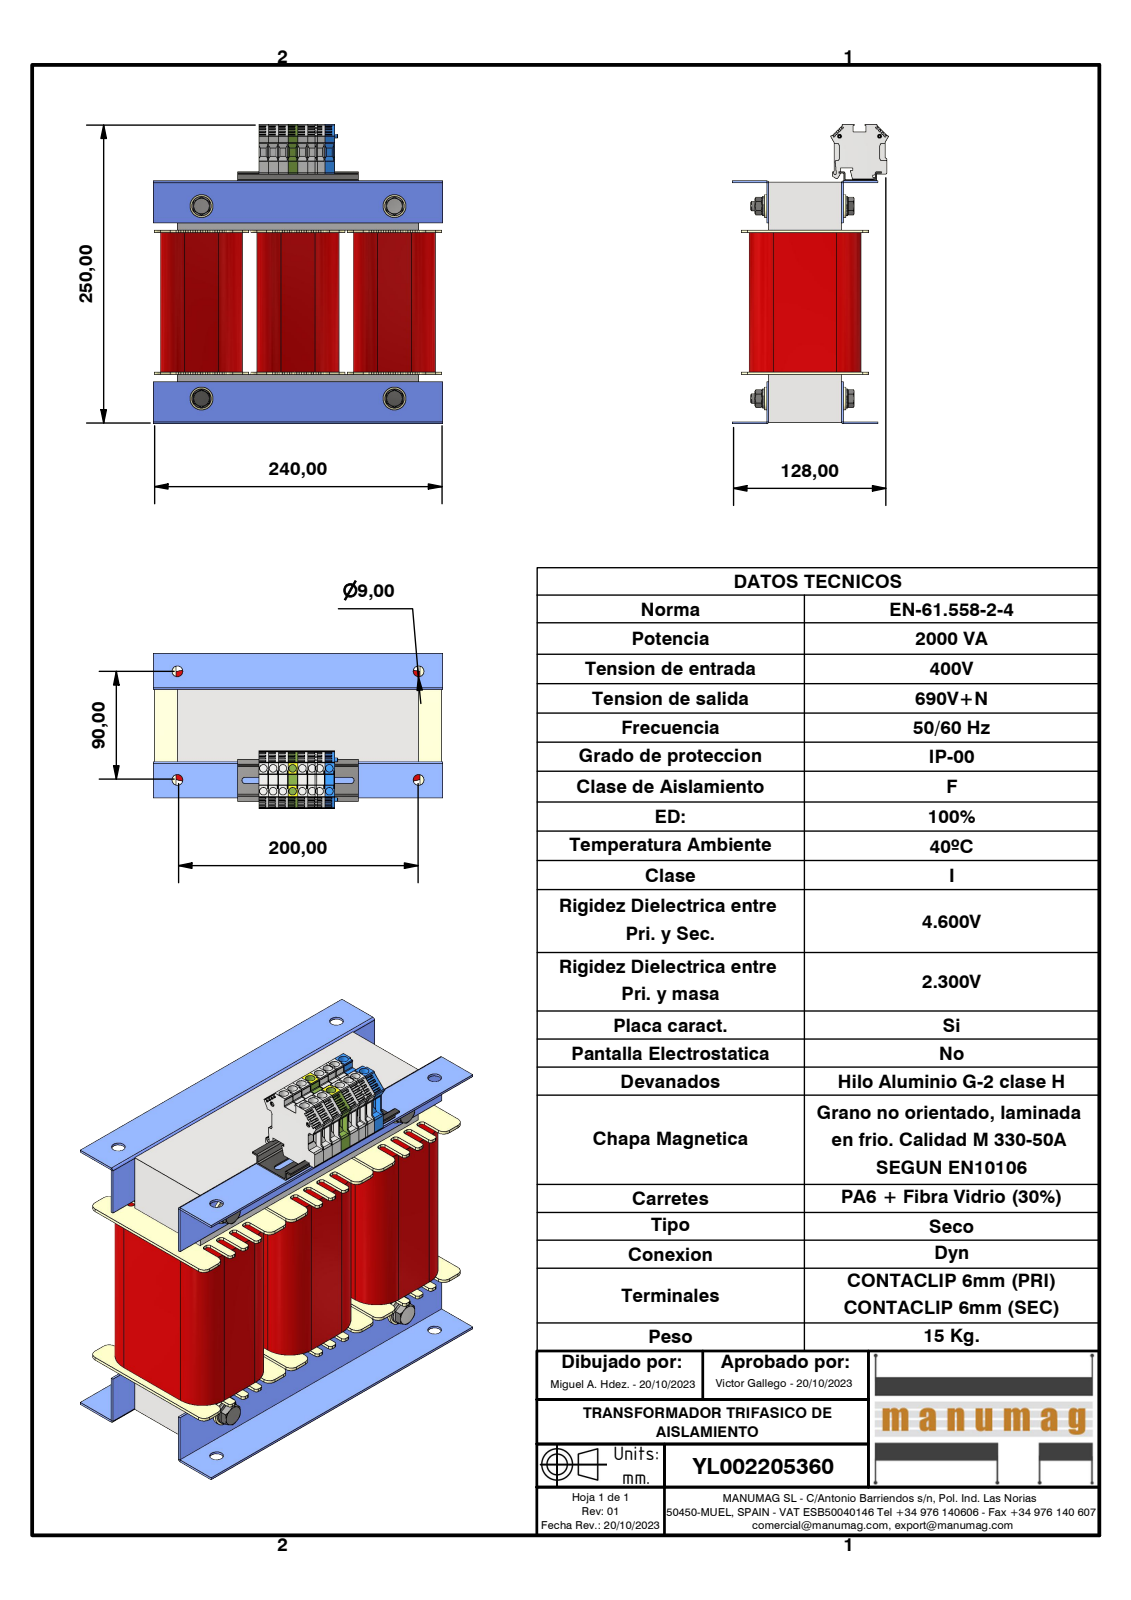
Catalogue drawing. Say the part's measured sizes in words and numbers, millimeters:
The part is named "YL002205360; 3UI120 200 x 200 - 60 (Rc40); UI 120_60; RC40 NT040 (+8 more)". Its 3-D file was written by "Autodesk Inventor 2023 (AUTOMOTIVE_DESIGN)". It is 41 solids with 2898 faces: 2018 planar, 712 cylindrical and 168 other. Overall it measures 249.05 by 240 by 128.9 millimeters. Its volume is 3 300 000 cubic millimeters and its surface area 582 876 square millimeters. Round holes: 16 of diameter 6.3, 4 of diameter 6.65, 4 of diameter 8, 4 of diameter 8.4, 4 of diameter 9, 4 of diameter 10.5, 4 of diameter 11, 2 of diameter 2.4, 2 of diameter 2.5, 2 of diameter 2.75, 2 of diameter 2.95. Round bosses or shafts: 4 of diameter 19, 4 of diameter 16, 4 of diameter 11.4, 4 of diameter 9.6, 4 of diameter 7.32. Partial cylindrical surfaces (rounded edges, fillets, slot ends): 85 of radius 2, 24 of radius 5, 16 of radius 0.25, 15 of radius 1, 12 of radius 20, 8 of radius 2.6, 5 of radius 0.3, 5 of radius 0.5. The main face-to-face distances are 40, 80, 160, 60, 120, 1.5, 14, 54, 61.5, 200. The hole center spacings are 8.1, 20.65, 16.2, 19, 24.97, 24.3, 30.85, 14.25.
